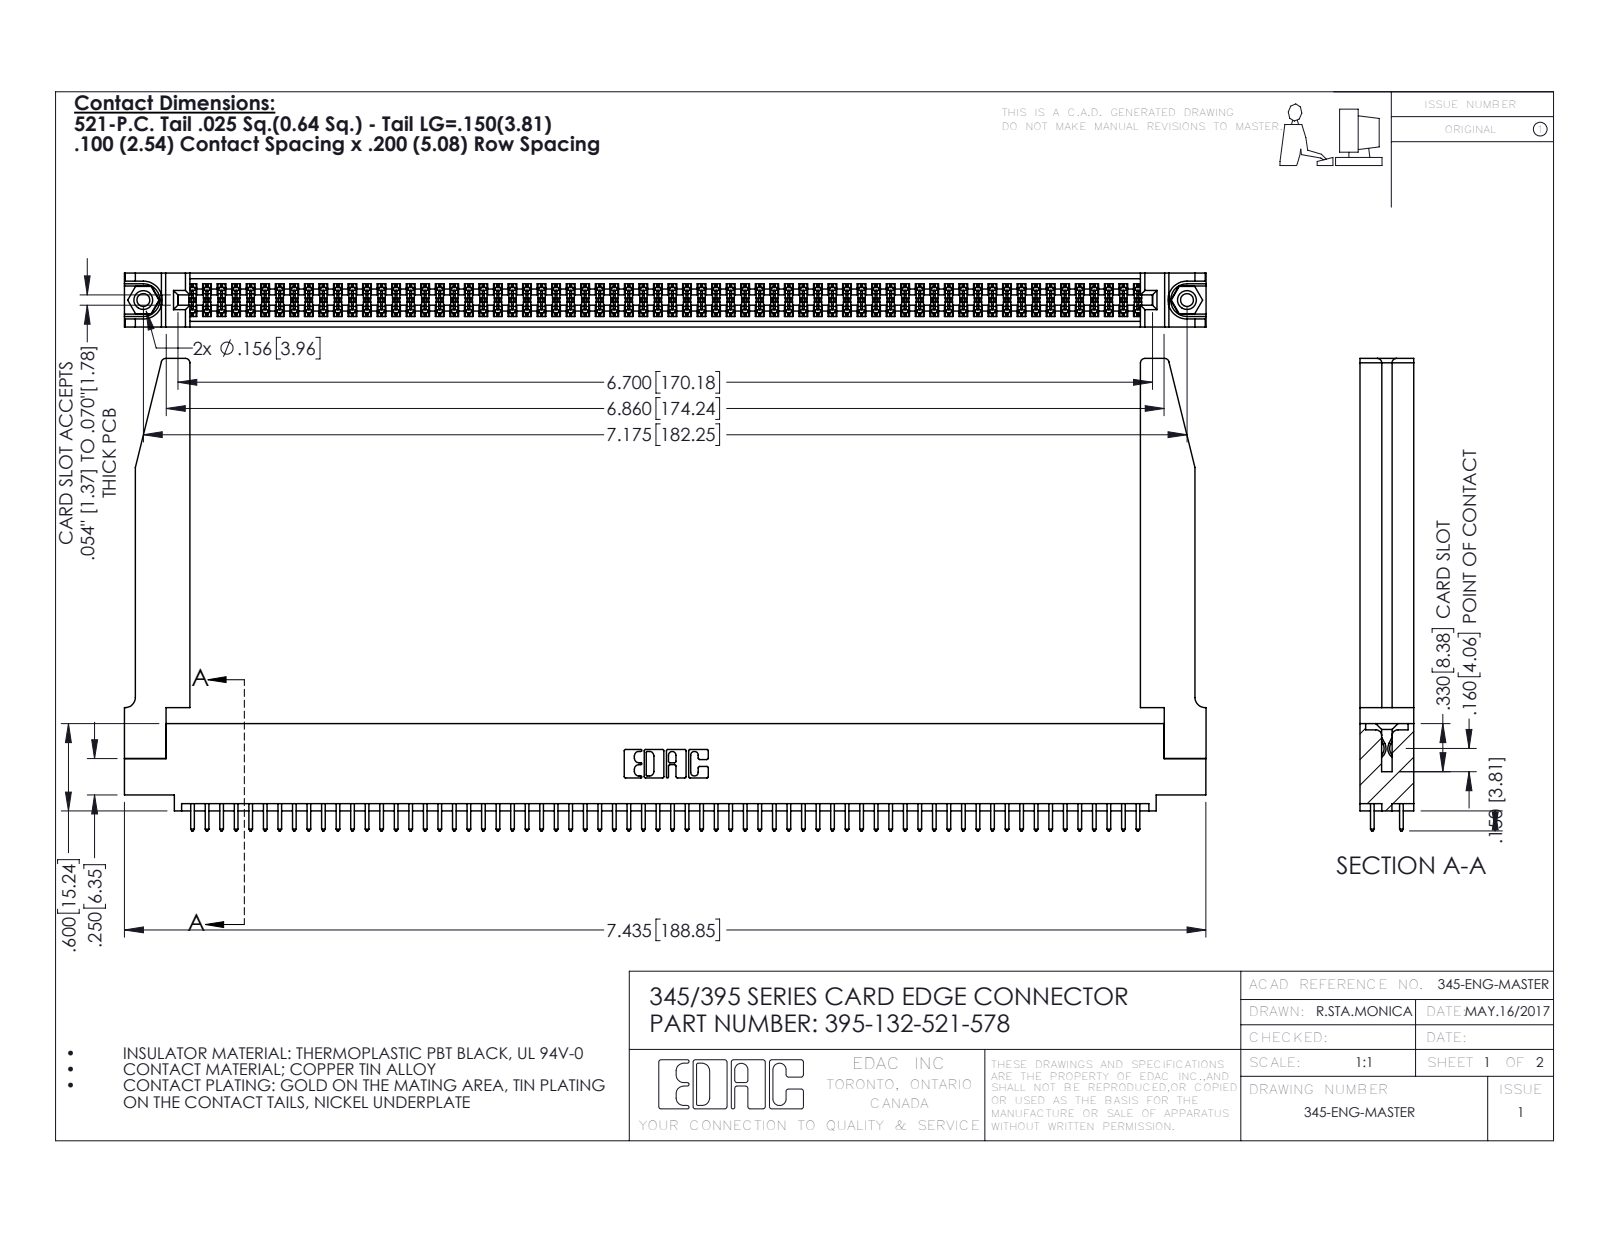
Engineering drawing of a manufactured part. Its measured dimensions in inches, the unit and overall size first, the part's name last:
Units: inches
Overall size (bounding box): 7.436 × 3.247 × 0.37
Round holes (diameter × count): ⌀0.089 ×2, ⌀0.125 ×2, ⌀0.156 ×2, ⌀0.064 ×1
Round bosses / shafts (diameter × count): ⌀0.155 ×2
Partial cylindrical surfaces — rounded edges, fillets, slot ends (radius × count): R0.006 ×198, R0.01 ×132, R0.01 ×22, R0.03 ×8, R0.007 ×6, R0.031 ×6, R0.026 ×3, R0.014 ×2
Main face-to-face distances: 0.072, 0.298, 0.37, 0.098, 0.272, 0.025, 0.2, 0.225, 0.175, 0.15
Hole centre spacings: 0.27, 6.939, 7.175
Volume: 1.6 in³ · Surface area: 53.18 in²
Bodies: 137 solids, 6964 faces (4582 planar, 2330 cylindrical, 52 other)
Part name (STEP PRODUCT): 345 Part_0.110 Offset - 0.156 Dia-TH; 345-250-001_345-250-001-102; 345-292-001_345-293-121; 345-220-078_345-220-078 (+1 more)
STEP written by: SolidWorks 2016 (CONFIG_CONTROL_DESIGN)
